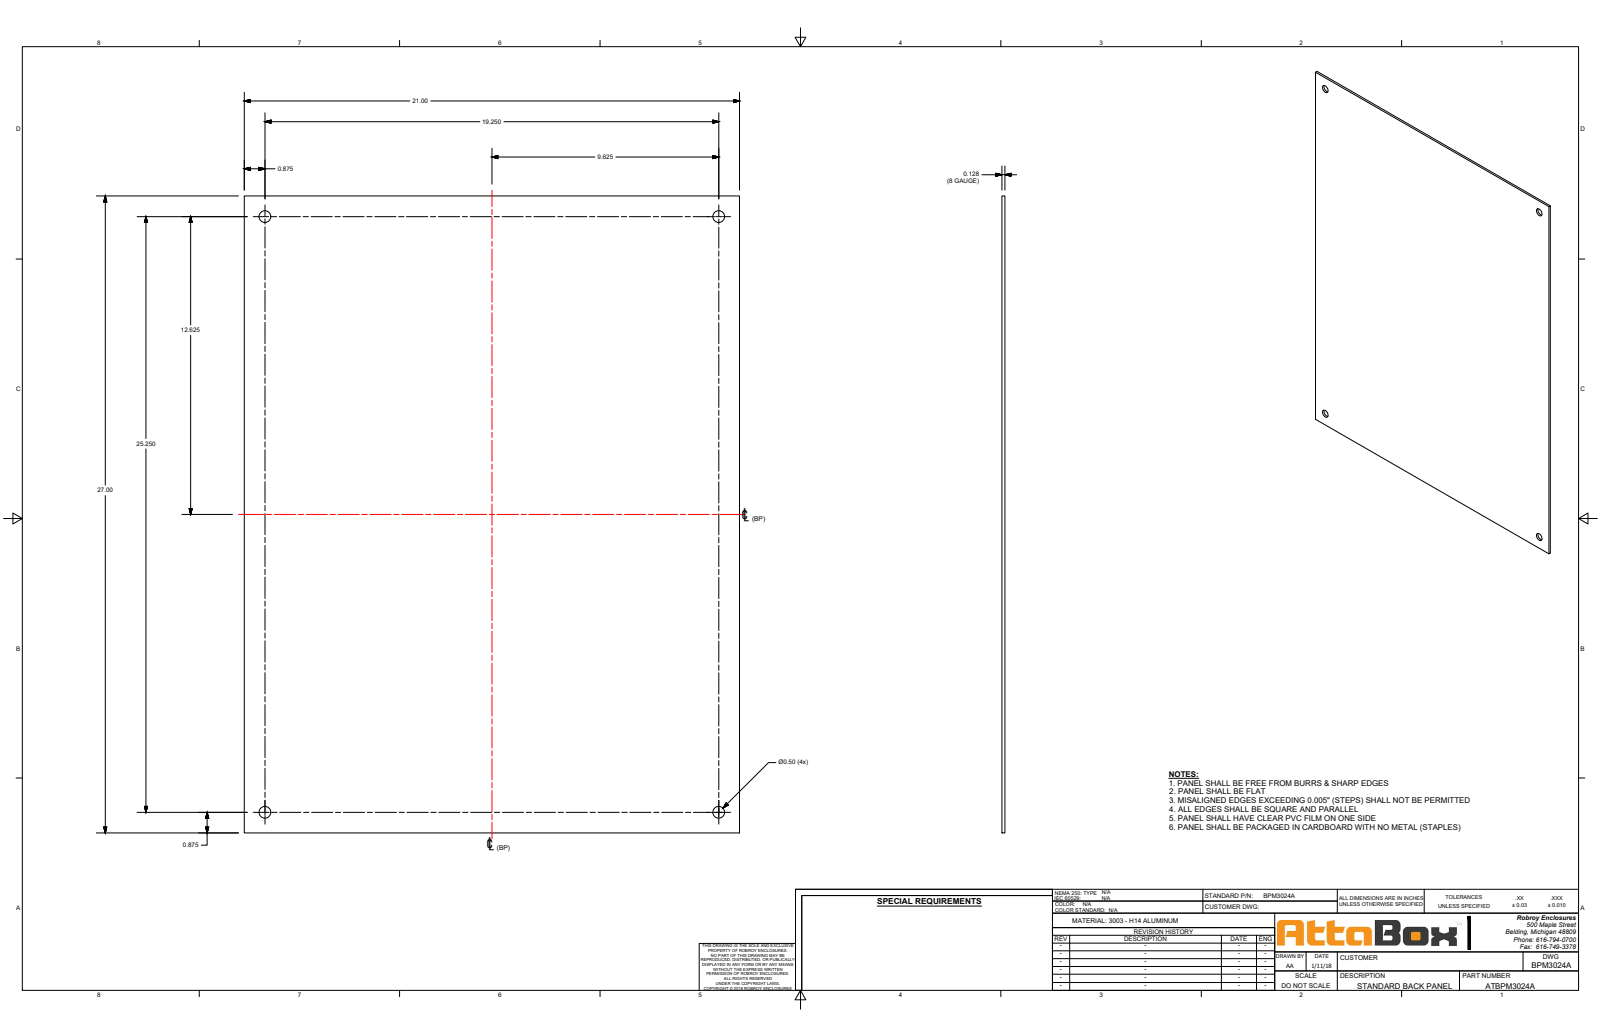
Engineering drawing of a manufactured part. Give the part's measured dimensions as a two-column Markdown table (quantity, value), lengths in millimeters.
| quantity | value |
| --- | --- |
| part name | BPM3024A |
| STEP written by | SolidWorks 2018 (AUTOMOTIVE_DESIGN) |
| units | millimeters |
| bodies | 1 solid, 10 faces (6 planar, 4 cylindrical, 0 other) |
| overall size | 685.8 × 533.4 × 3.3 |
| volume | 1 188 000 mm³ |
| surface area | 739 400 mm² |
| round holes (diameter × count) | 12.7 × 4 |
| main face-to-face distances | 3.3, 533.4, 685.8 |
| hole center spacings | 489, 641.4, 806.5 |
